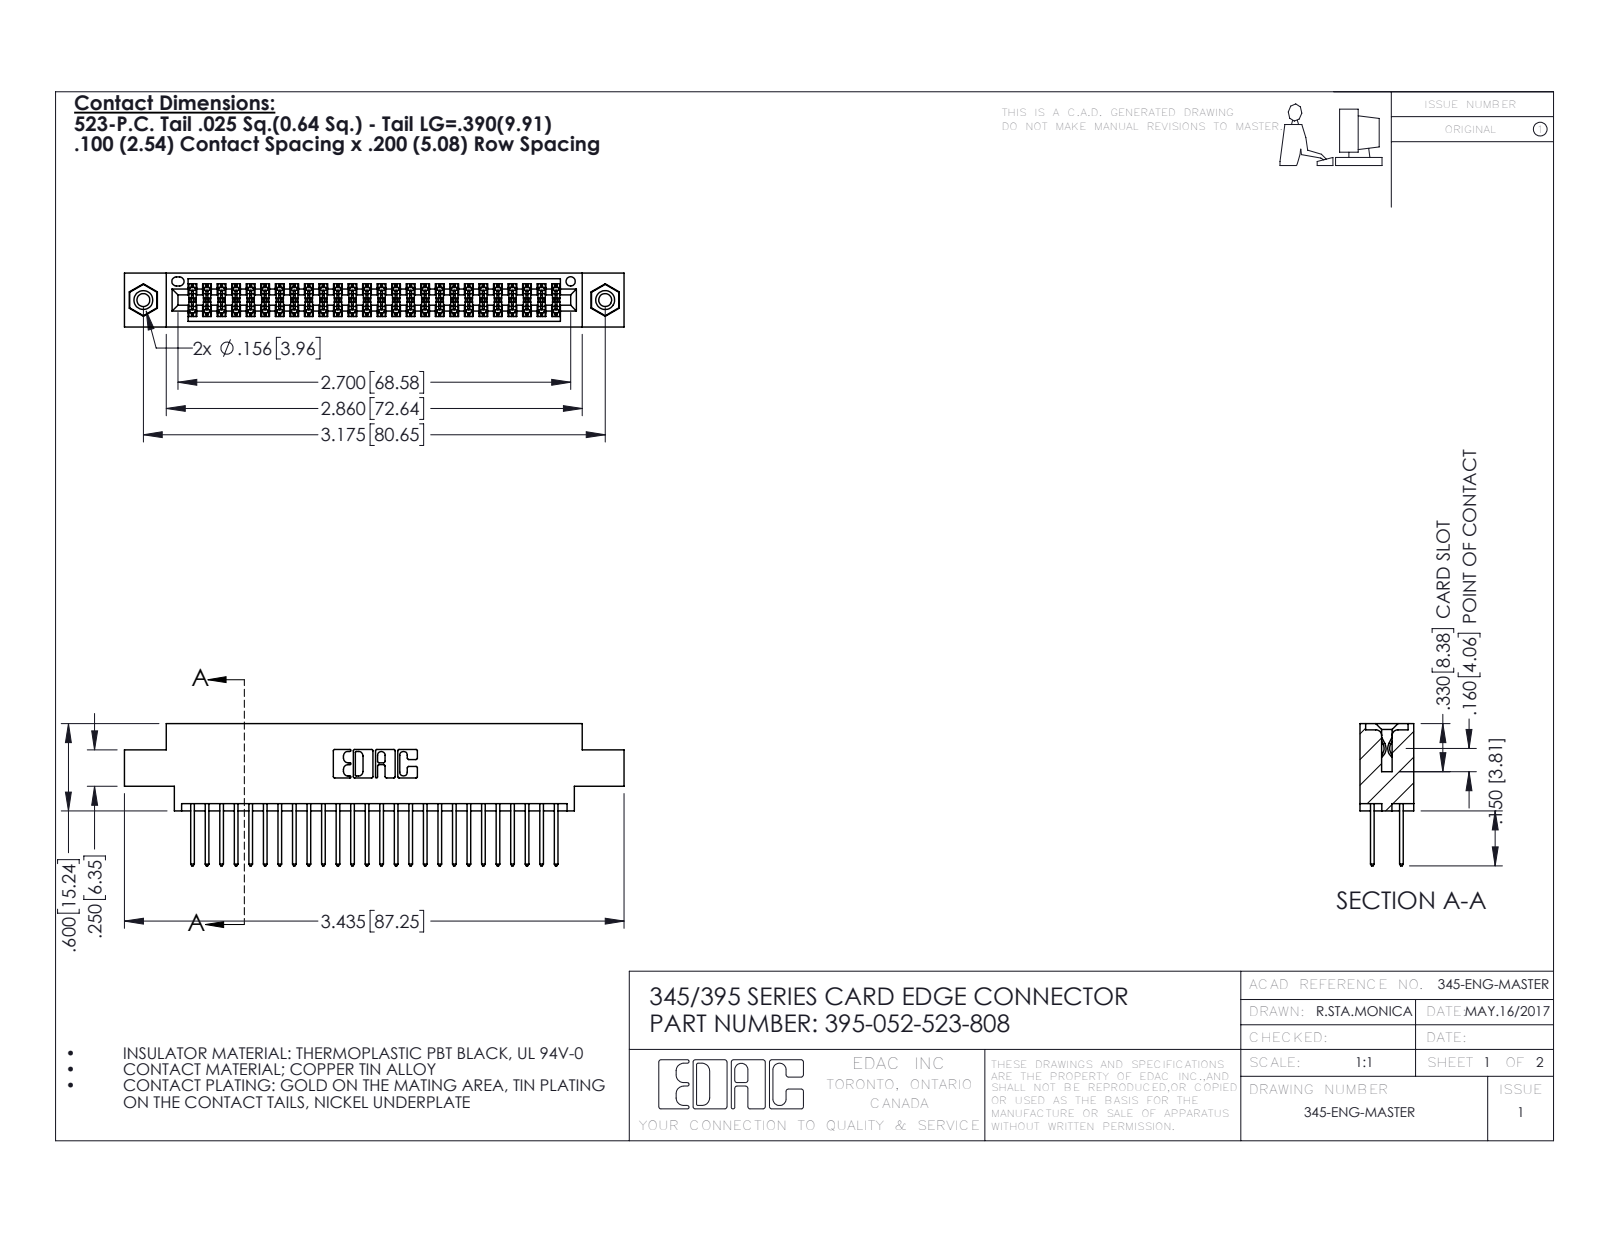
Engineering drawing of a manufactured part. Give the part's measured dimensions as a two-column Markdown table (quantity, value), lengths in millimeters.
| quantity | value |
| --- | --- |
| part name | 395-052-523-808; 345-250-001_345-250-003-102; 345 Part_0.170 Offset - 0.156 Dia-TI; 345-292-001_345-293-123 |
| STEP written by | SolidWorks 2016 (CONFIG_CONTROL_DESIGN) |
| units | millimeters |
| bodies | 55 solids, 2790 faces (1832 planar, 942 cylindrical, 16 other) |
| overall size | 87.2 × 24.8 × 9.4 |
| volume | 8 310 mm³ |
| surface area | 12 610 mm² |
| round holes (diameter × count) | 2.3 × 2, 3.2 × 2, 4 × 2, 1.6 × 1 |
| round bosses / shafts (diameter × count) | 3.9 × 2 |
| partial cylindrical surfaces (radius × count) | 0.2 × 78, 0.3 × 52, 0.3 × 22, 0.2 × 6, 0.8 × 6, 0.7 × 3, 0.4 × 2, 0.5 × 2 |
| main face-to-face distances | 1.8, 7.6, 5.1, 2.5, 6.9, 0.6, 9.4, 5.7, 4.4, 3.8 |
| hole center spacings | 6.9, 74.7, 80.6 |
